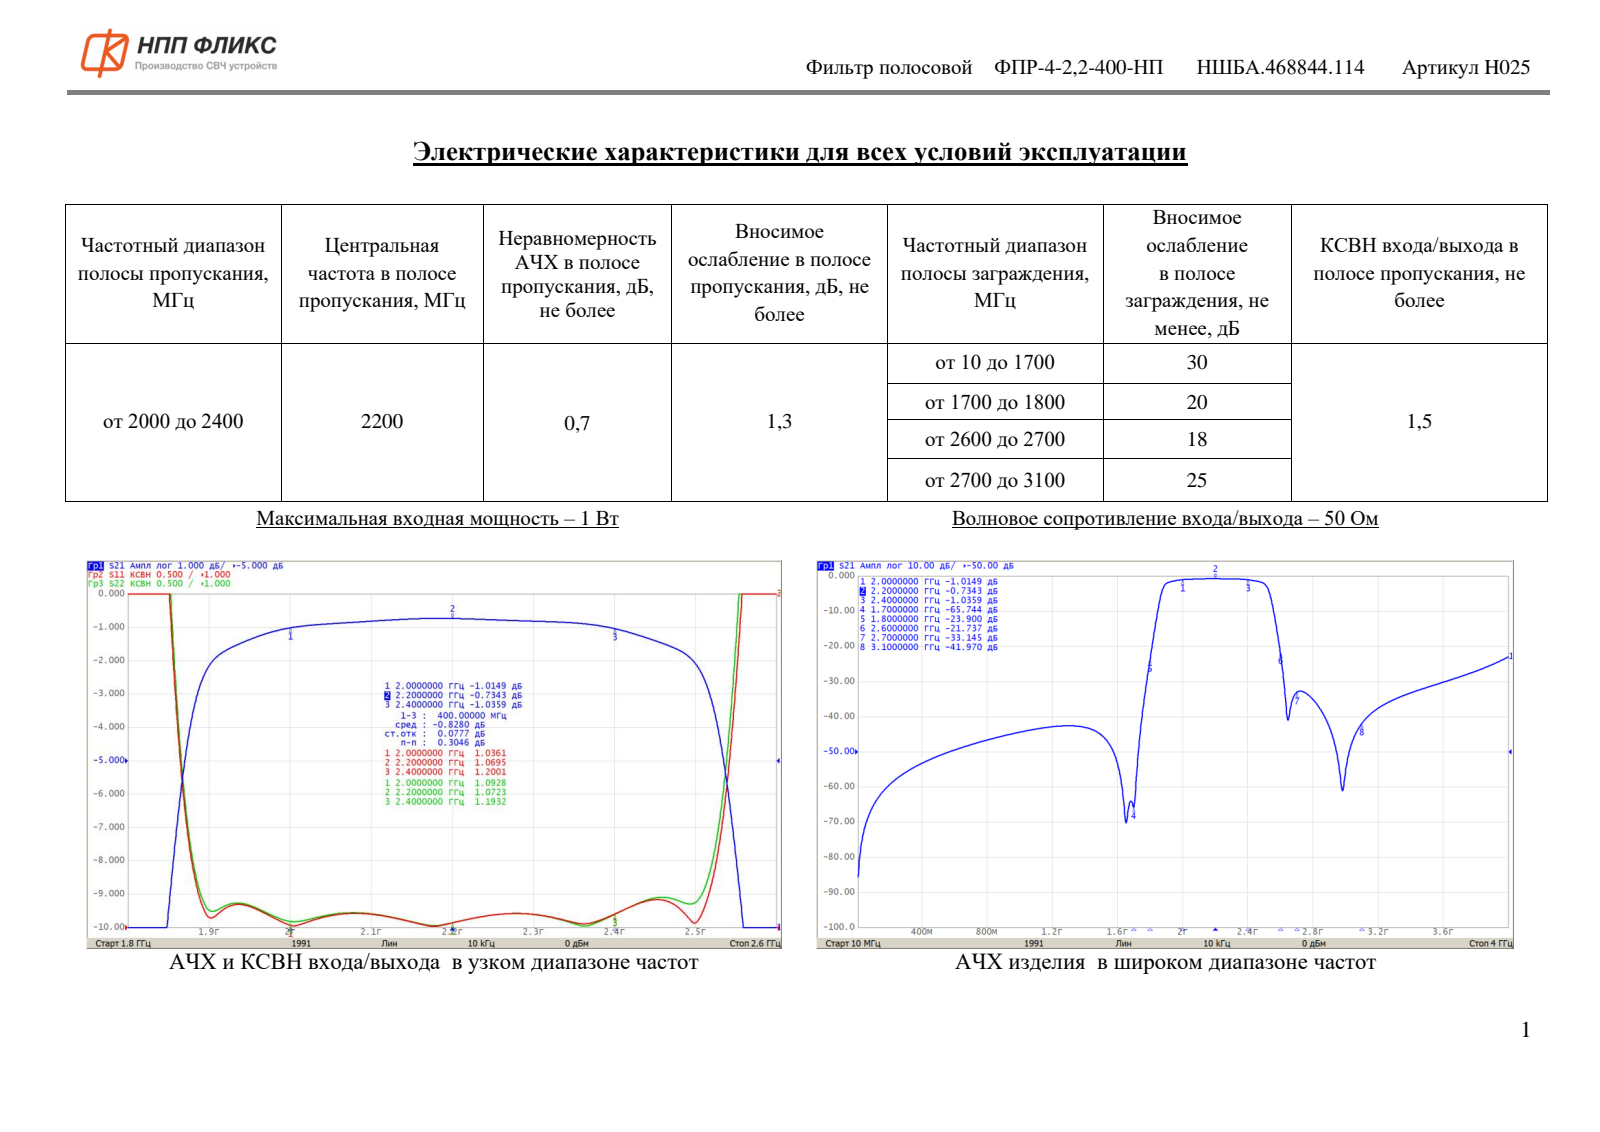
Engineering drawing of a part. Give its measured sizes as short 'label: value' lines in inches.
name: НШБА.468844.114_Фильтр ФПР-4-2,2-400-НП
written by: ASCON Math Kernel (CONFIG_CONTROL_DESIGN)
unit: in
bodies: 2 solids, 494 faces (359 planar, 27 cylindrical, 108 other)
size: 0.748 × 0.591 × 0.169
volume: 0.024 in³; area: 2.227 in²
rounds: 8× R0.018, 4× R0.012, 4× R0.024, 3× R0.011, 1× R0.006, 1× R0.017, 1× R0.019
face distances: 0.039, 0.118, 0.13, 0.157, 0.169, 0.535, 0.697, 0.033, 0.022, 0.557
